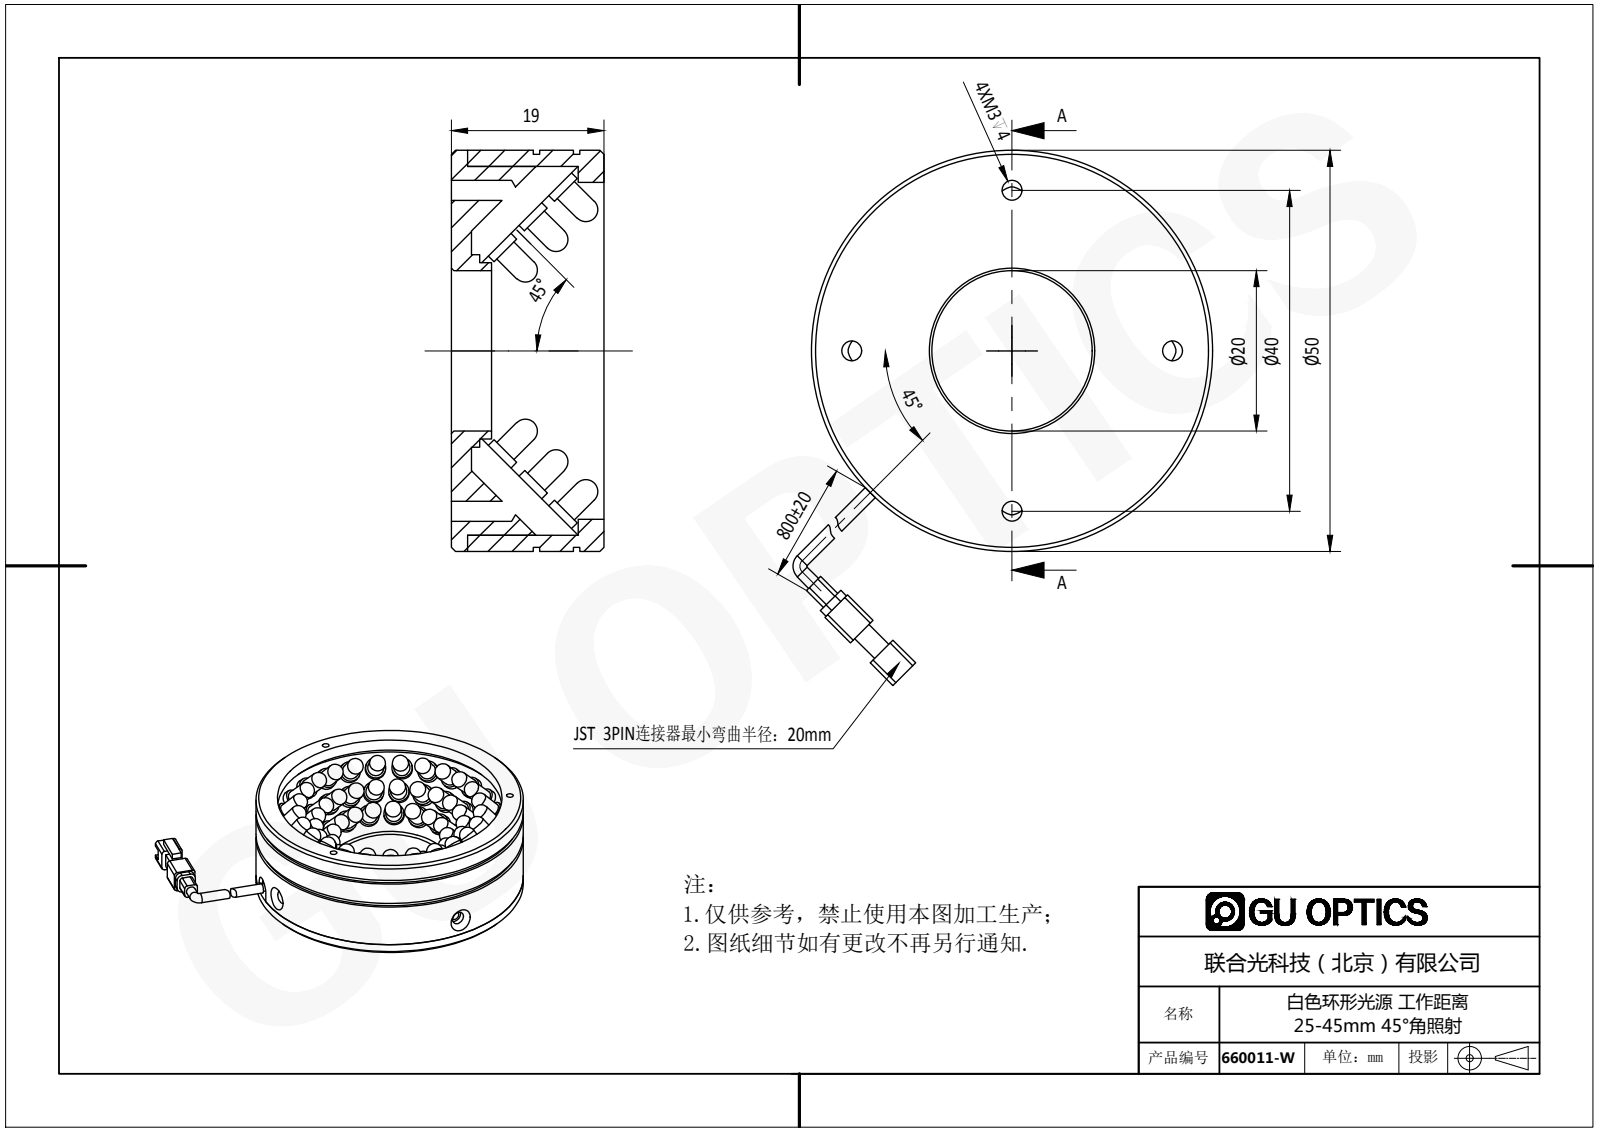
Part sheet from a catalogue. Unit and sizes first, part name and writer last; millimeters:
Units: millimetres
Overall size (bounding box): 66.72 × 52.33 × 19
Round holes (diameter × count): ⌀2.5 ×4, ⌀1.25 ×3, ⌀3 ×3, ⌀1.6 ×2, ⌀2.4 ×2, ⌀20 ×1, ⌀42 ×1
Round bosses / shafts (diameter × count): ⌀3.8 ×65, ⌀3 ×63, ⌀1.75 ×2, ⌀50 ×1, ⌀49 ×1, ⌀46 ×1, ⌀24 ×1, ⌀22 ×1
Partial cylindrical surfaces — rounded edges, fillets, slot ends (radius × count): R0.5 ×10, R1 ×4, R1.6 ×1, R4.5 ×1
Main face-to-face distances: 2, 0.5, 19, 17, 2.5, 1, 3, 16.5, 5, 0.8
Hole centre spacings: 20, 28.28, 22.5, 38.97, 11.26, 30.1, 40, 2.5
Volume: 17 436 mm³ · Surface area: 21 875 mm²
Bodies: 70 solids, 1331 faces (857 planar, 361 cylindrical, 113 other)
Part name (STEP PRODUCT): 660011-W
STEP written by: SolidWorks 2016 (AUTOMOTIVE_DESIGN)
